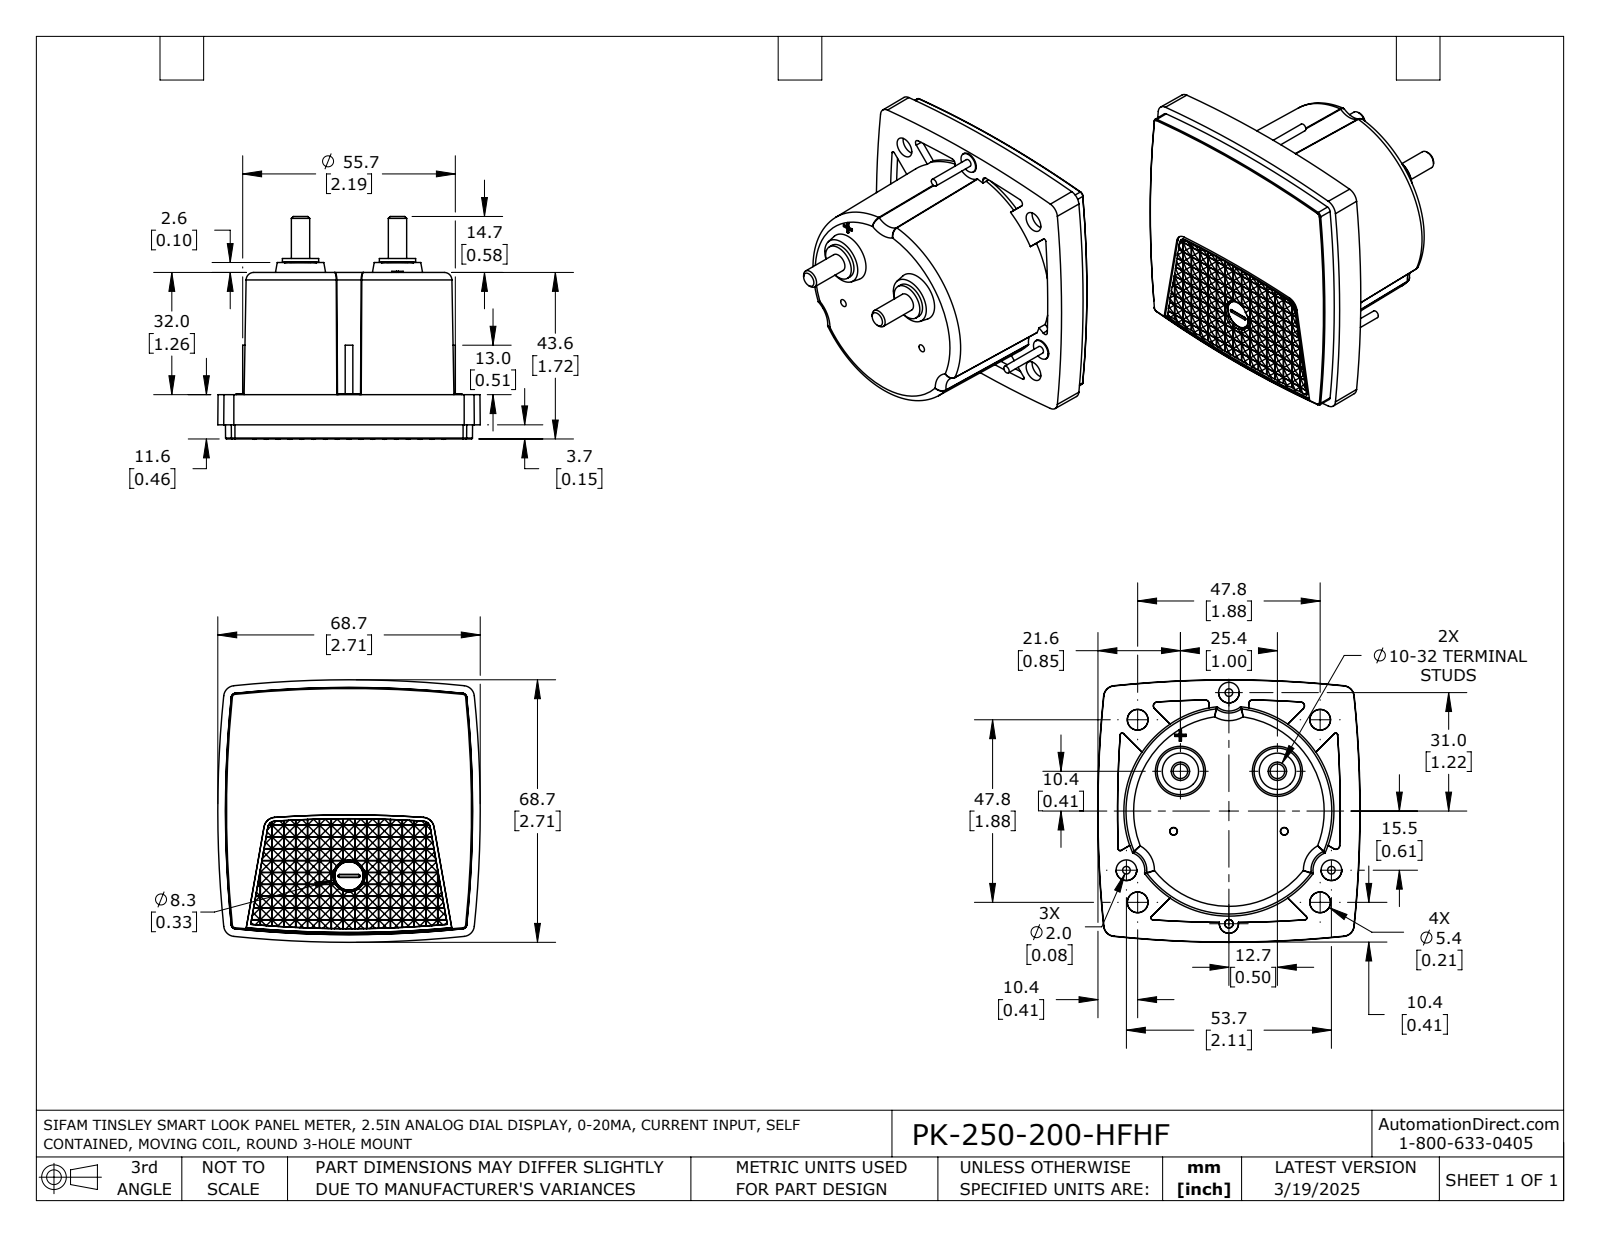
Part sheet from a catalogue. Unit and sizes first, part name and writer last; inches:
Units: inches
Overall size (bounding box): 2.706 × 2.706 × 2.297
Round bosses / shafts (diameter × count): ⌀0.213 ×3, ⌀0.079 ×3, ⌀0.374 ×2, ⌀0.189 ×2, ⌀0.215 ×1
Partial cylindrical surfaces — rounded edges, fillets, slot ends (radius × count): R0.167 ×2, R1.083 ×1
Main face-to-face distances: 1.717, 1.26, 0.457, 0.024, 0.087, 0.096, 0.311, 0.12, 0.072, 1.346
Volume: 7.594 in³ · Surface area: 30.41 in²
Bodies: 1 solid, 1550 faces (1165 planar, 265 cylindrical, 120 other)
Part name (STEP PRODUCT): PK-250-200-HFHF
STEP written by: SolidWorks 2021 (AUTOMOTIVE_DESIGN)
